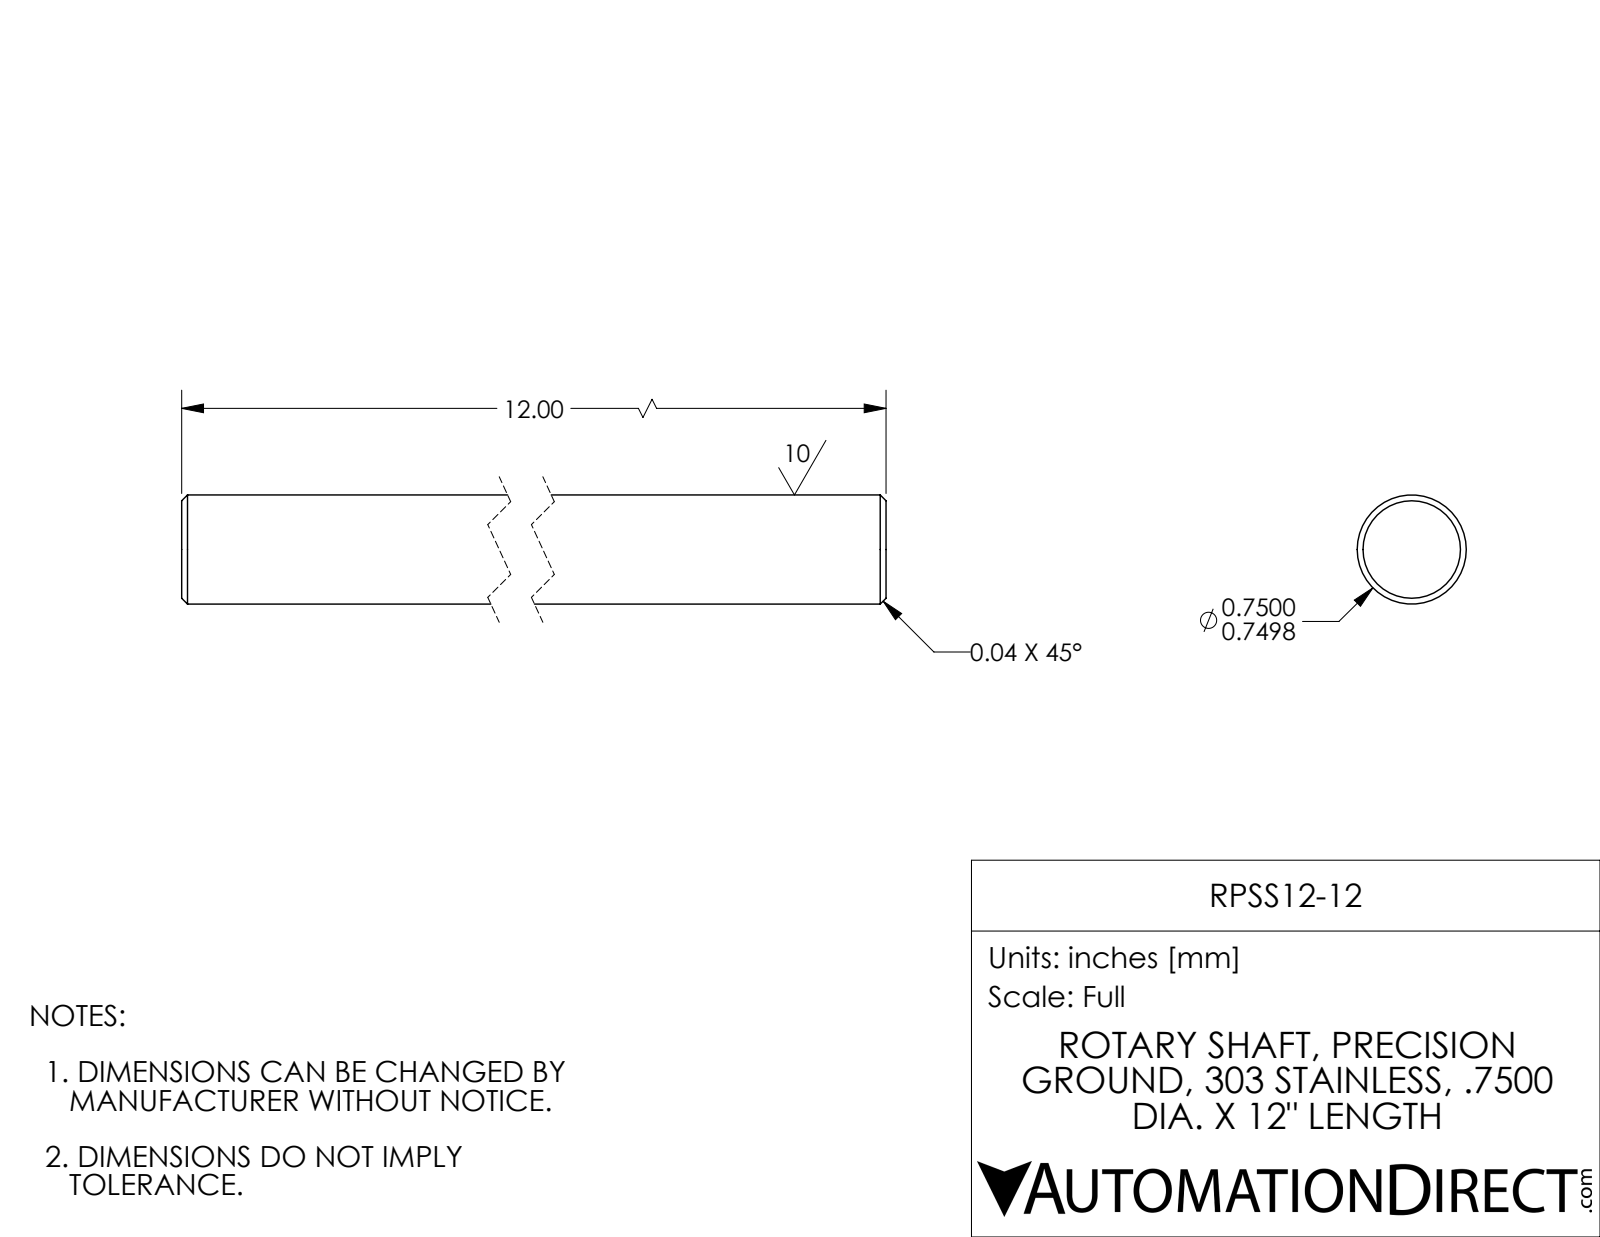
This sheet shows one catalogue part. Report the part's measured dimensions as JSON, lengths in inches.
{"part_name": "RPSS12-12", "step_written_by": "SolidWorks 2017 (AUTOMOTIVE_DESIGN)", "units": "inches", "bodies": {"solids": 1, "faces": 8, "planar": 2, "cylindrical": 2, "other": 4}, "overall_size": [12, 0.75, 0.75], "volume_in3": 5.298, "surface_area_in2": 29.04, "round_bosses_or_shafts": [[0.75, 1]], "face_to_face_distances": [12]}
